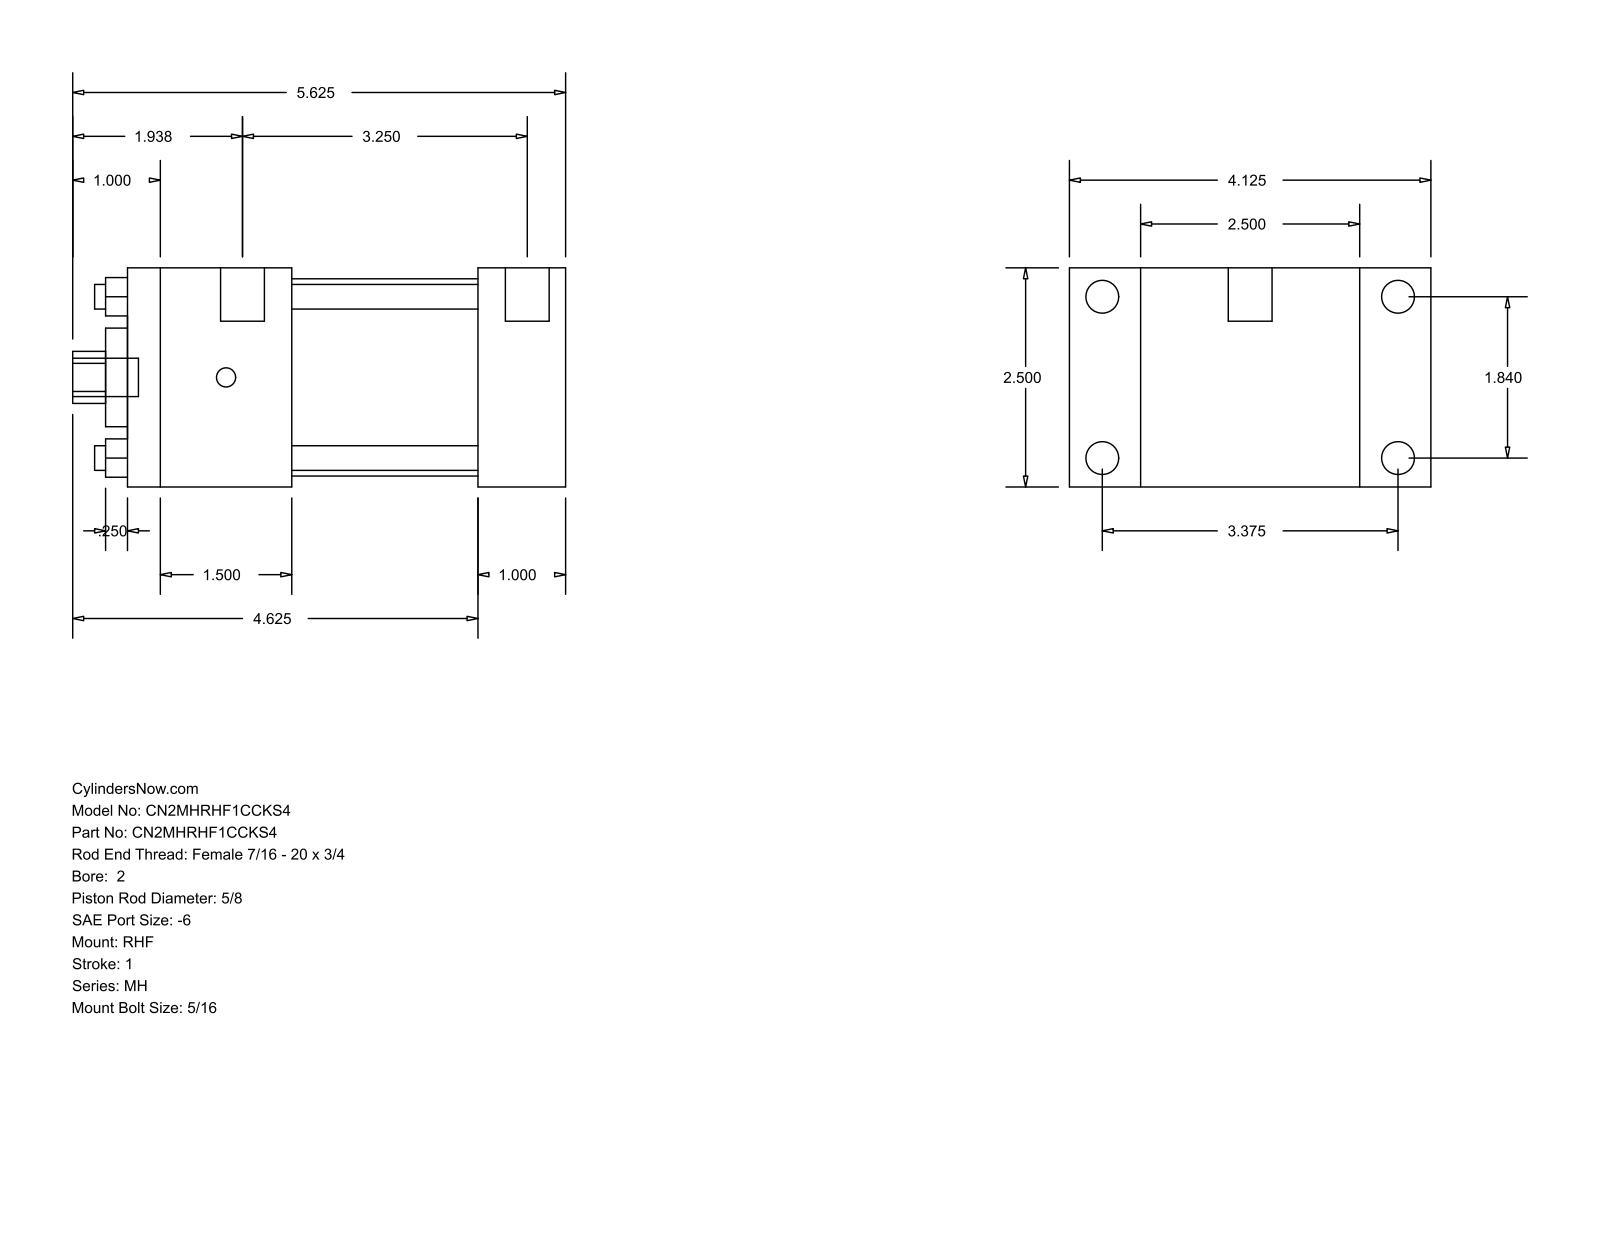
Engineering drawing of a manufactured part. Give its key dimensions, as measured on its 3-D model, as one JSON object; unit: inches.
{"part_name": "MH_RHF__0200_0.625", "step_written_by": "GSSL Pune (CONFIG_CONTROL_DESIGN)", "units": "inches", "bodies": {"solids": 0, "faces": 88, "planar": 60, "cylindrical": 28, "other": 0}, "overall_size": [5.625, 4.125, 2.5], "round_holes": [[0.281, 4], [0.625, 1], [1.125, 1], [2.25, 1]], "round_bosses_or_shafts": [[0.375, 4], [0.219, 4], [0.5, 2], [0.437, 1]], "partial_cylinders_radius": [[0.297, 1]], "face_to_face_distances": [2.5, 1, 0.813, 3.313, 4, 5, 2.125, 4.125, 1.875, 3.125], "hole_center_spacings": [1.301, 1.84, 2.602]}
